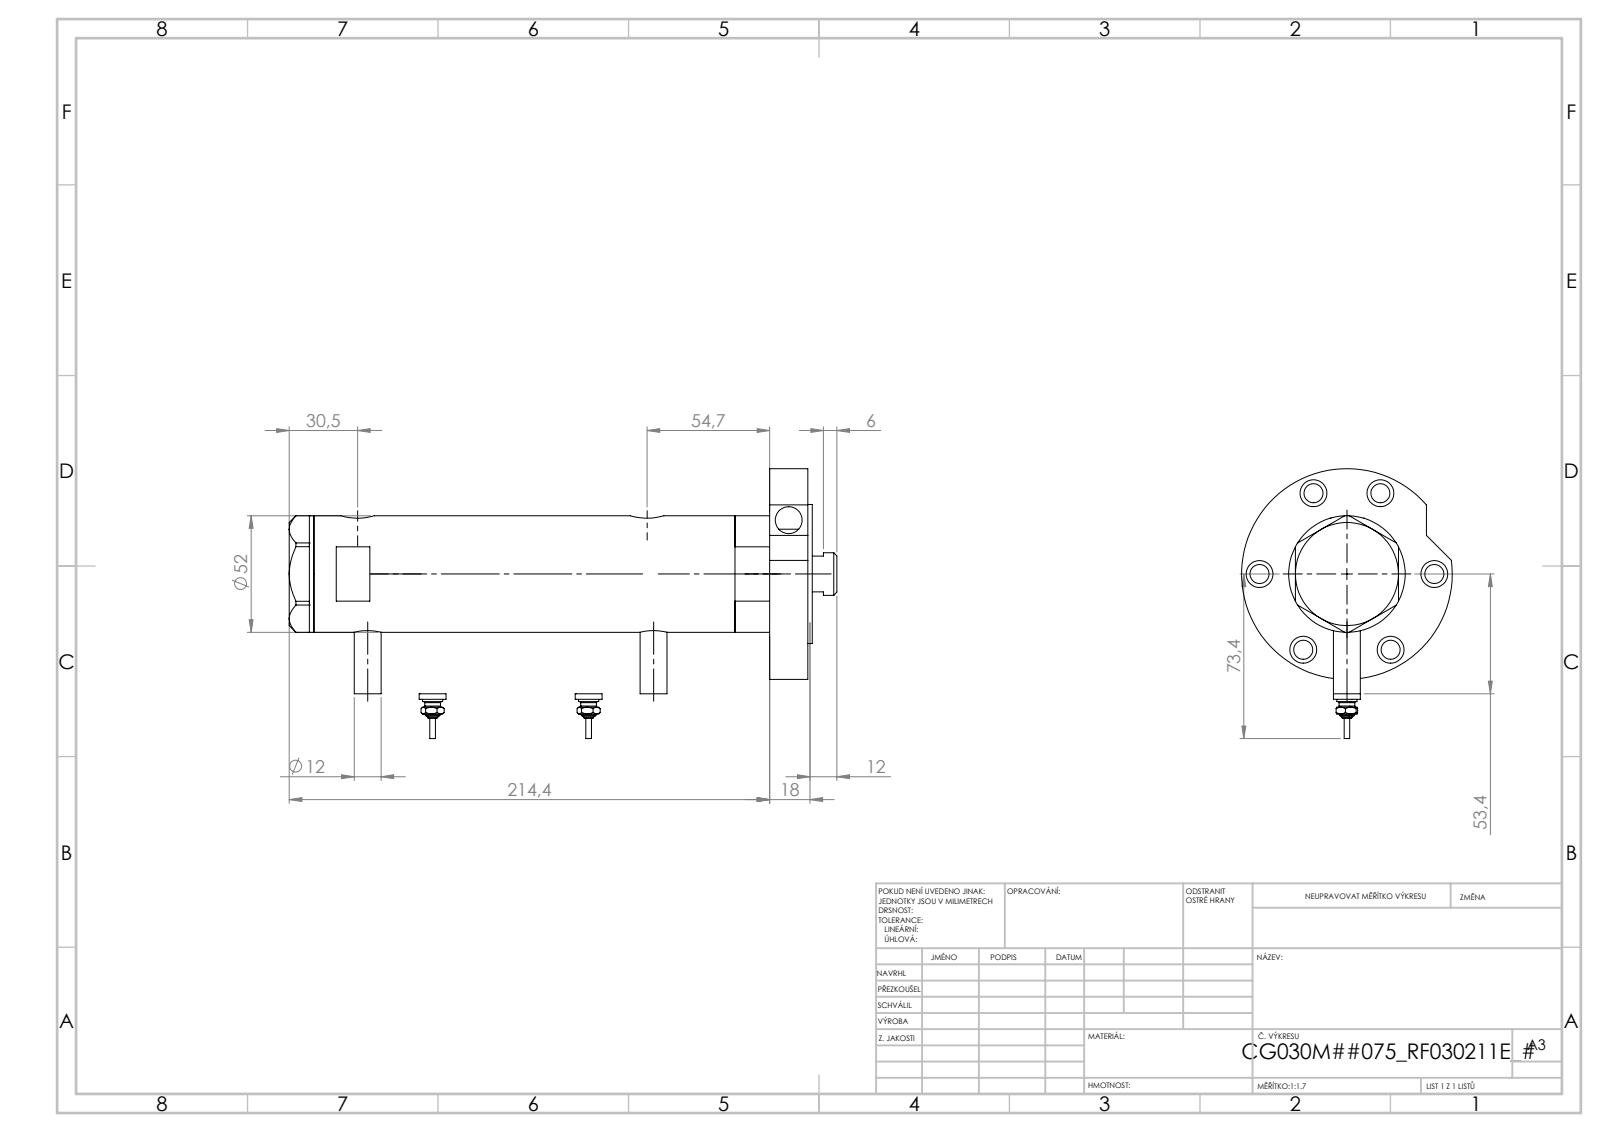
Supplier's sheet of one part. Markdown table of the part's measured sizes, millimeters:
| quantity | value |
| --- | --- |
| part name | V270CG_FRONT; V270CG_MIDDLE; V270CG_RF211E; V270CG_SWITCH (+2 more) |
| STEP written by | SolidWorks 2019 (CONFIG_CONTROL_DESIGN) |
| units | millimeters |
| bodies | 7 solids, 290 faces (106 planar, 110 cylindrical, 74 other) |
| overall size | 224.02 × 105.3 × 94 |
| volume | 482 013 mm³ |
| surface area | 114 851 mm² |
| round holes (diameter × count) | 12 × 7, 8.5 × 6, 5 × 2, 9.73 × 2, 12.5 × 2, 15 × 2, 6.5 × 1, 20 × 1, 21.5 × 1, 30 × 1, 33 × 1, 40 × 1 |
| round bosses / shafts (diameter × count) | 12 × 3, 9 × 2, 7 × 2, 4.34 × 2, 2.4 × 2, 94 × 1, 62 × 1, 52 × 1 |
| main face-to-face distances | 17, 180.44, 197.44, 51.9, 2, 199.44, 128.54, 68.9, 70.9, 19 |
| hole center spacings | 39, 2.9, 4.5, 43.34, 64.85, 67.55, 69.95, 77.83 |
